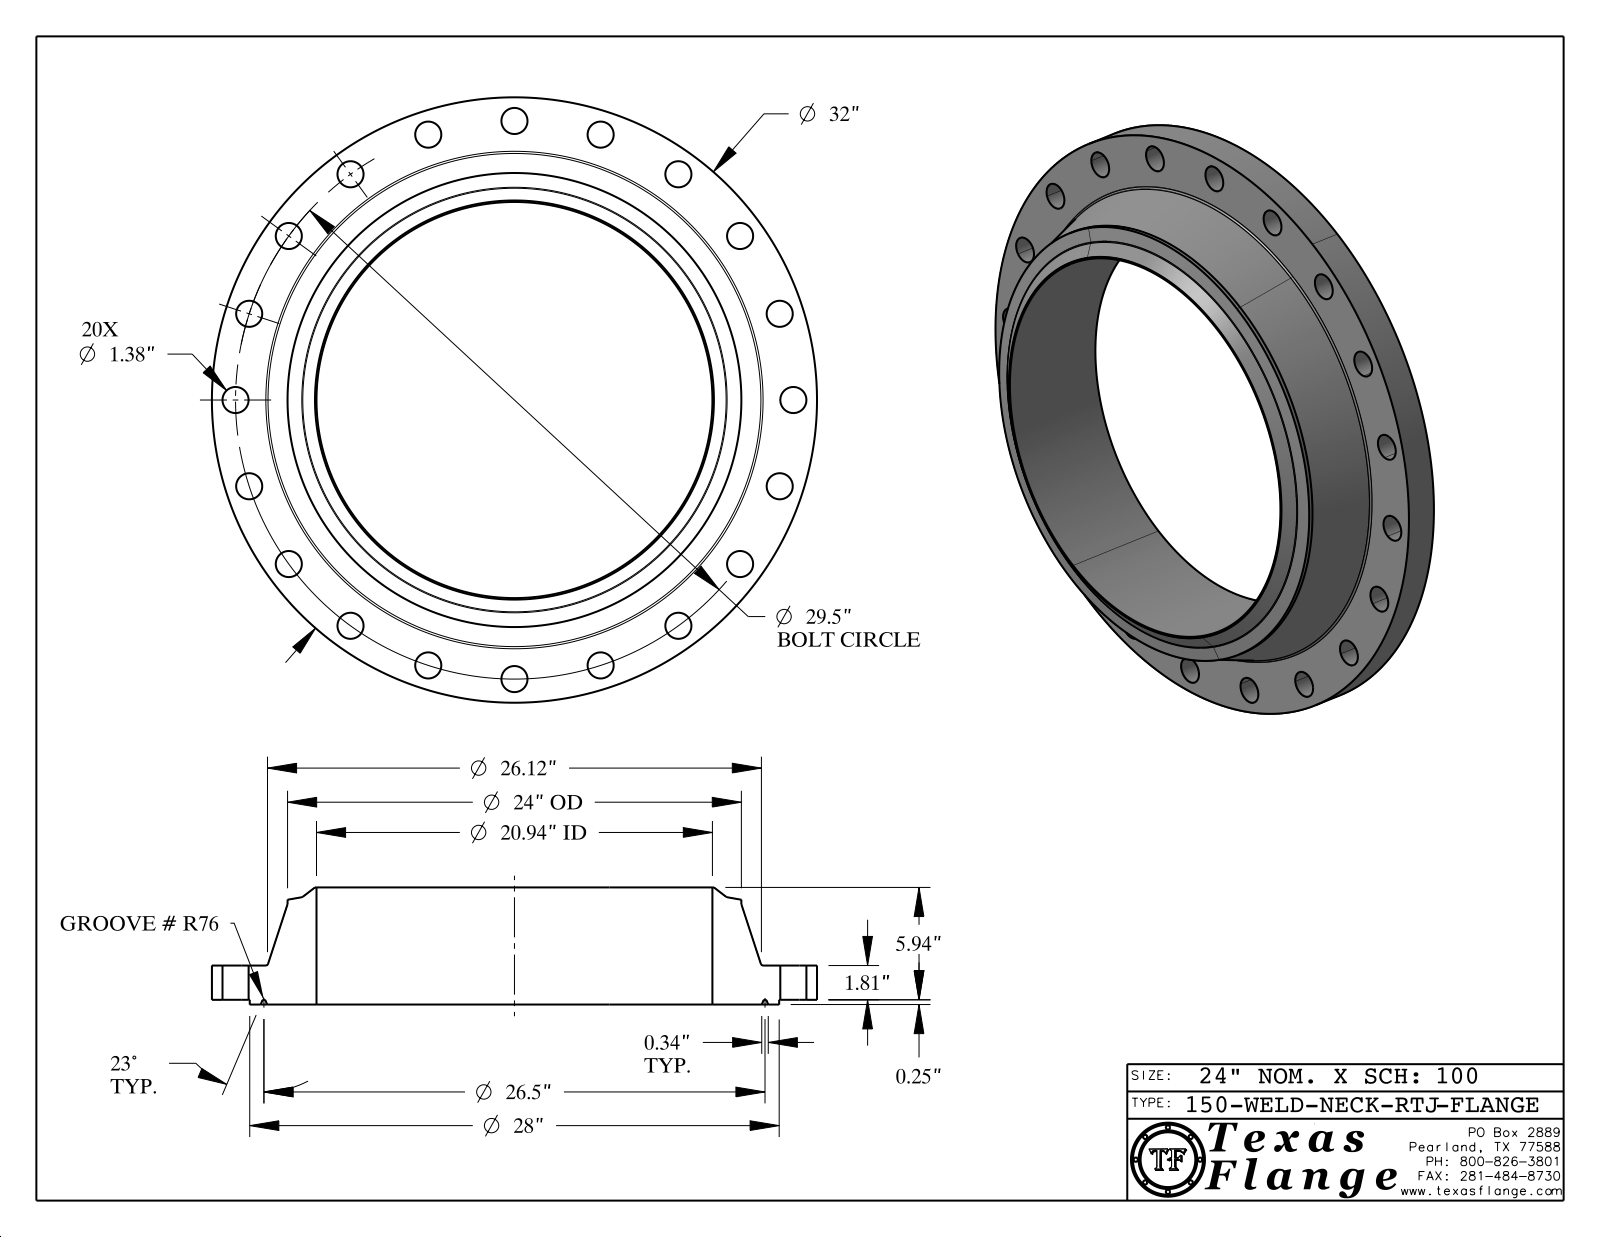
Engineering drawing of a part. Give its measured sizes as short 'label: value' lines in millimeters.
name: 150-WELD-NECK-RTJ
written by: CATIA V5 STEP AP214 (AUTOMOTIVE_DESIGN)
unit: mm
bodies: 1 solid, 457 faces (371 planar, 68 cylindrical, 18 other)
size: 812.8 × 812.8 × 157.2
volume: 22 550 000 mm³; area: 1 206 000 mm²
holes: 20× ⌀35.1, 1× ⌀12.6, 1× ⌀531.8
bosses: 8× ⌀0.8, 1× ⌀812.8, 1× ⌀711.2, 1× ⌀609.6, 1× ⌀9.9
face distances: 52.3, 6.4, 46, 157.2, 150.9, 104.9, 52.2, 45.8, 105, 3.8
hole spacings: 374.7, 740.1, 117.2, 440.4, 529.8, 606.2, 667.6, 231.5
